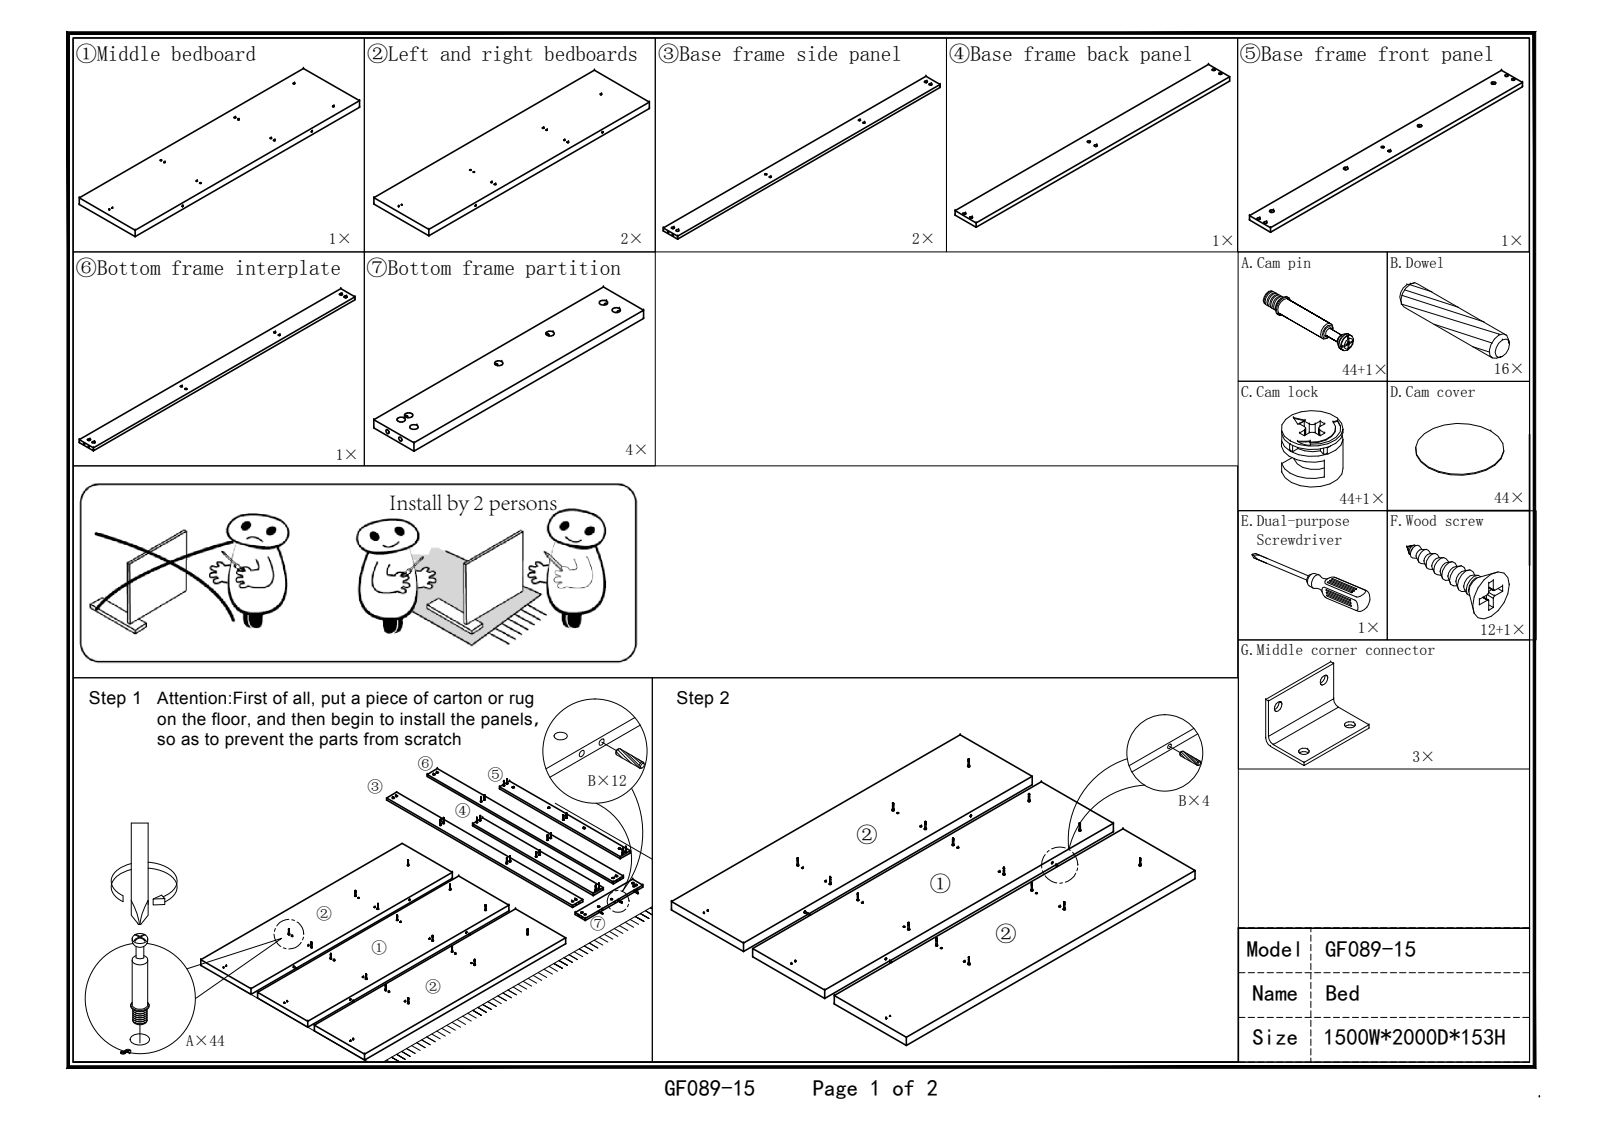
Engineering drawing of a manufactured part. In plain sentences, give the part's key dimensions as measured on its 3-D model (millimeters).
Its 3-D file was written by "ACIS (automotive_design)". It is 2 solids with 35 faces: 9 planar, 16 cylindrical and 10 other. Overall it measures 95 by 16 by 16 millimeters. Its volume is 14 022 cubic millimeters and its surface area 7 164 square millimeters. Round holes: 1 of diameter 12.94. Round bosses or shafts: 1 of diameter 16, 1 of diameter 12.5. Partial cylindrical surfaces (rounded edges, fillets, slot ends): 1 of radius 0.9, 1 of radius 1.48, 1 of radius 2.04, 1 of radius 6.24. The main face-to-face distances are 32, 95, 63, 0.58, 67.92, 35.92, 27.08.
